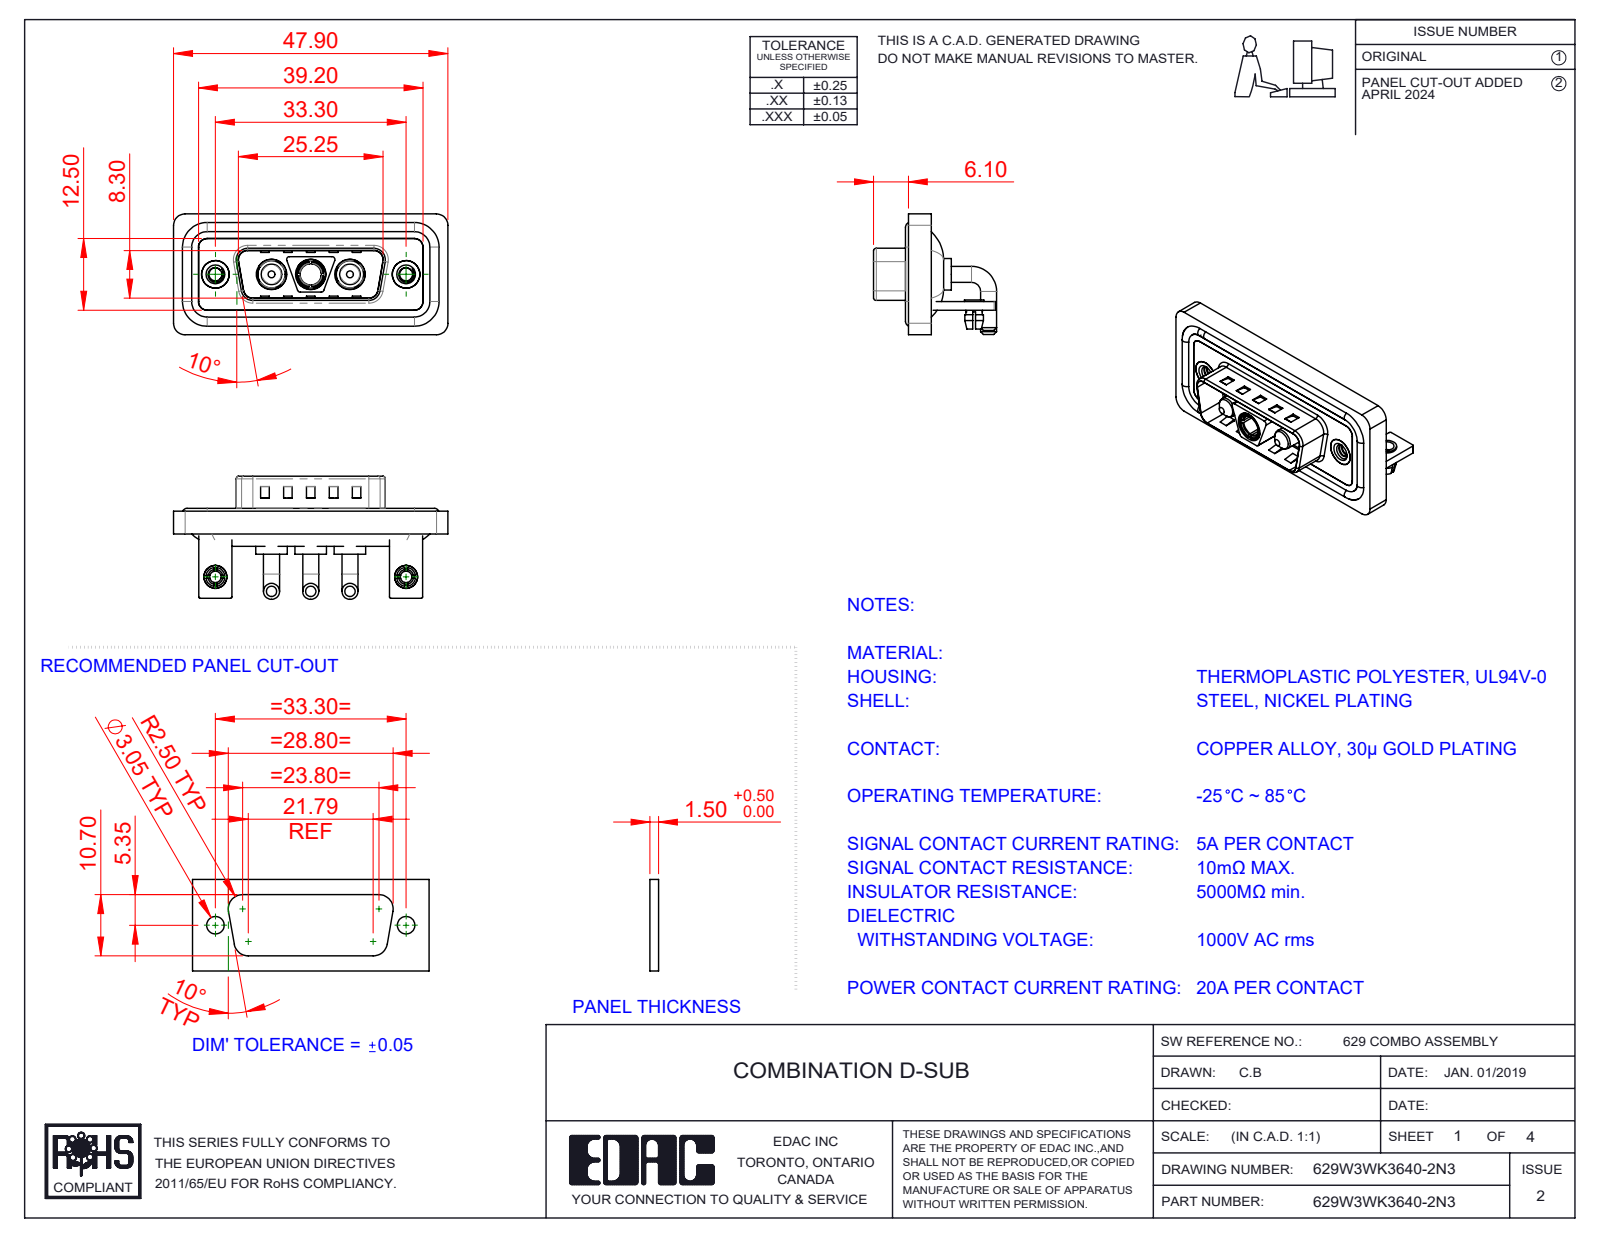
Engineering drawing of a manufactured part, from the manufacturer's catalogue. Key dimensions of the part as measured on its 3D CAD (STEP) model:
Part name (STEP PRODUCT): 629Combo Shell Rear_15 Contacts; 629Combo Threaded Rivet_3; 629Combo Stabilizer Bracket; 629Combo Shell Front_15 Contacts (+6 more)
STEP written by: SolidWorks 2023 (CONFIG_CONTROL_DESIGN)
Units: millimetres
Bodies: 17 solids, 753 faces (299 planar, 306 cylindrical, 148 other)
Overall size (bounding box): 47.9 × 21.5 × 21.1
Volume: 6 199 mm³ · Surface area: 10 213 mm²
Round holes (diameter × count): ⌀4.85 ×3, ⌀5.3 ×3, ⌀2 ×2, ⌀2.26 ×2, ⌀2.5 ×2, ⌀3.2 ×2, ⌀4 ×2, ⌀4.8 ×2, ⌀5 ×2, ⌀3.7 ×1
Round bosses / shafts (diameter × count): ⌀2.8 ×6, ⌀1.6 ×4, ⌀5.5 ×3, ⌀5.2 ×3, ⌀4.75 ×3, ⌀3.75 ×3, ⌀4.9 ×2, ⌀4 ×2
Partial cylindrical surfaces — rounded edges, fillets, slot ends (radius × count): R2 ×21, R1.5 ×18, R0.25 ×16, R0.5 ×13, R1.6 ×8, R0.6 ×4, R0.65 ×4, R0.9 ×4
Main face-to-face distances: 0.4, 1.5, 0.8, 2.9, 1.1, 2.1, 3.7, 1.6, 1.2, 4.5
Hole centre spacings: 6.85, 9.8, 16.65, 23.5, 33.3, 13.7
